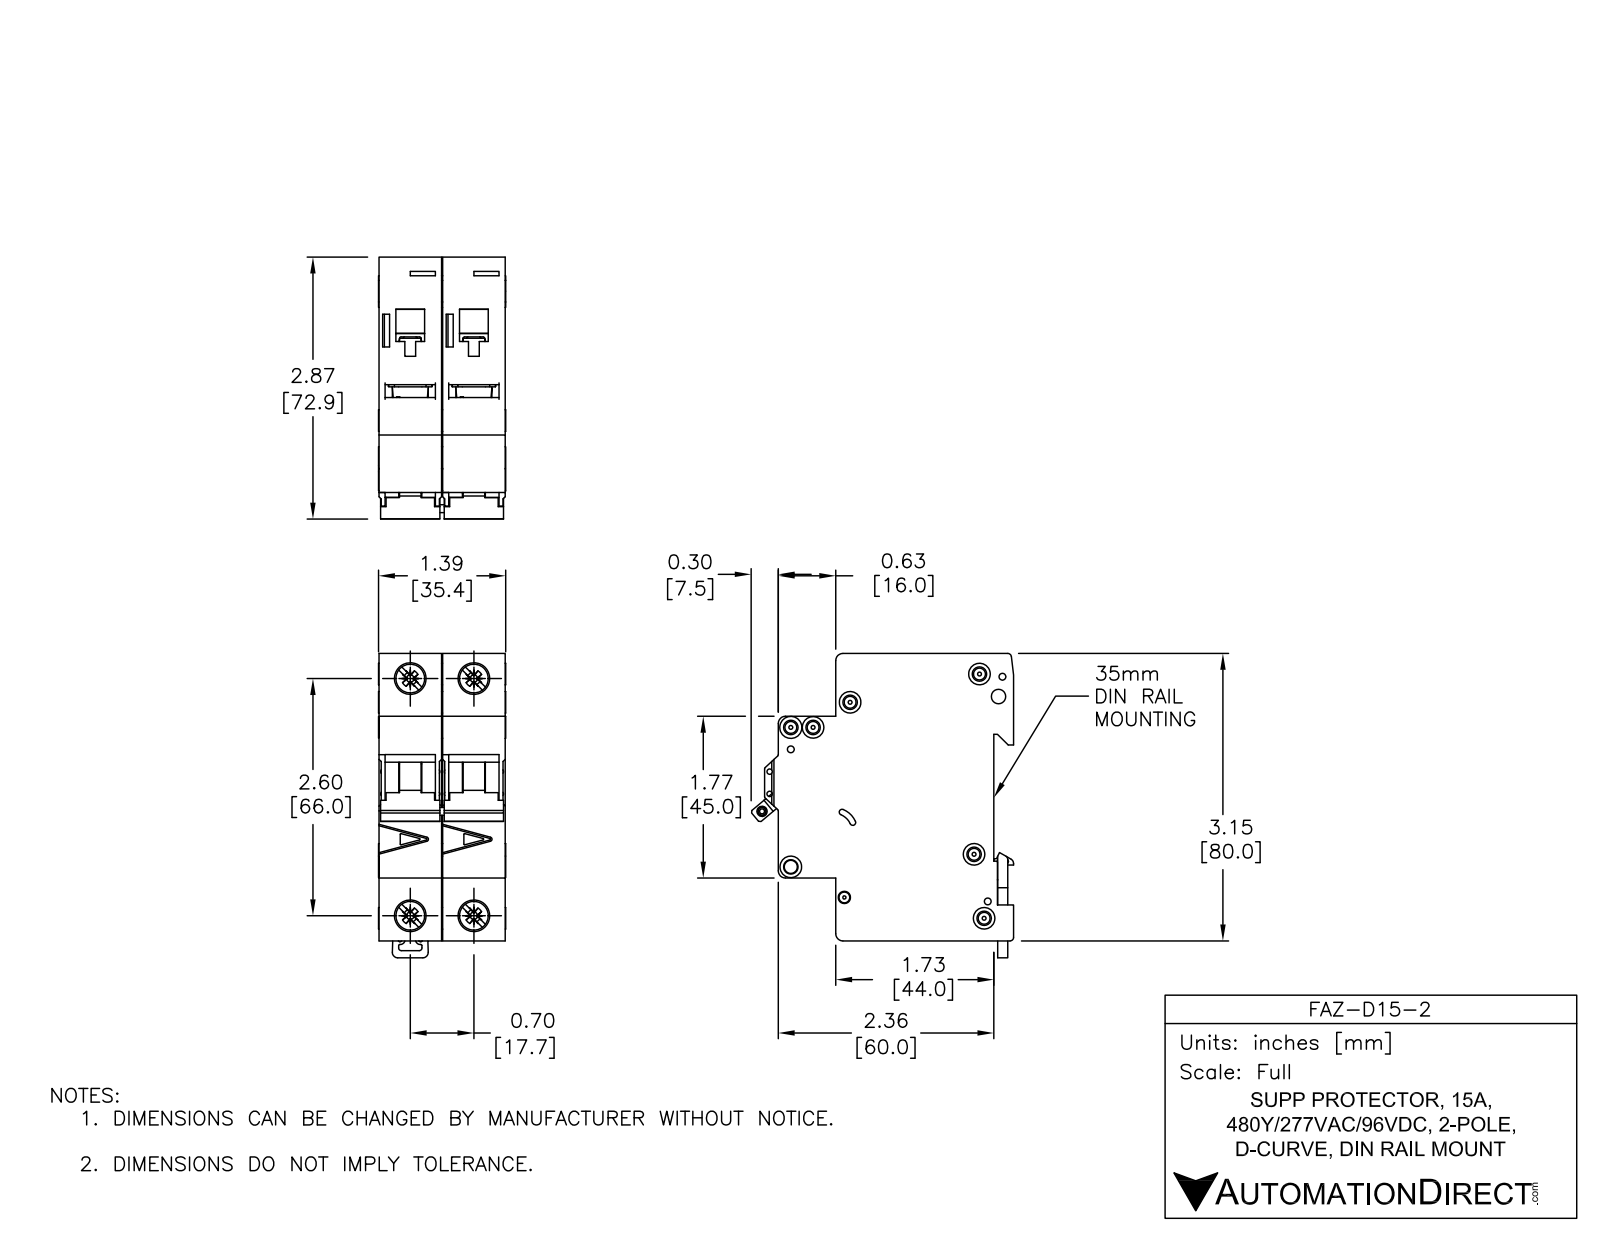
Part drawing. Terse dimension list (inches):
name: FAZ-D15-2
written by: SolidWorks 2014 (AUTOMOTIVE_DESIGN)
unit: in
bodies: 8 solids, 1104 faces (466 planar, 396 cylindrical, 242 other)
size: 3.338 × 2.876 × 1.394
volume: 9.142 in³; area: 60.14 in²
holes: 6× ⌀0.142, 3× ⌀0.075, 2× ⌀0.043, 2× ⌀0.059, 2× ⌀0.157, 2× ⌀0.281, 2× ⌀0.323, 1× ⌀0.085, 1× ⌀0.087, 1× ⌀0.1, 1× ⌀0.13, 1× ⌀0.134
bosses: 4× ⌀0.236, 2× ⌀0.323, 2× ⌀0.098
rounds: 49× R0.01, 19× R0.02, 10× R0.079, 8× R0.008, 8× R0.039, 2× R0.031, 2× R0.071, 2× R0.118
face distances: 0.697, 0.689, 1.386, 3.129, 0.217, 1.949, 1.732, 2.579, 2.362, 0.63
hole spacings: 0.244, 0.537, 0.697, 2.598, 2.69, 0.189, 0.204, 0.221
